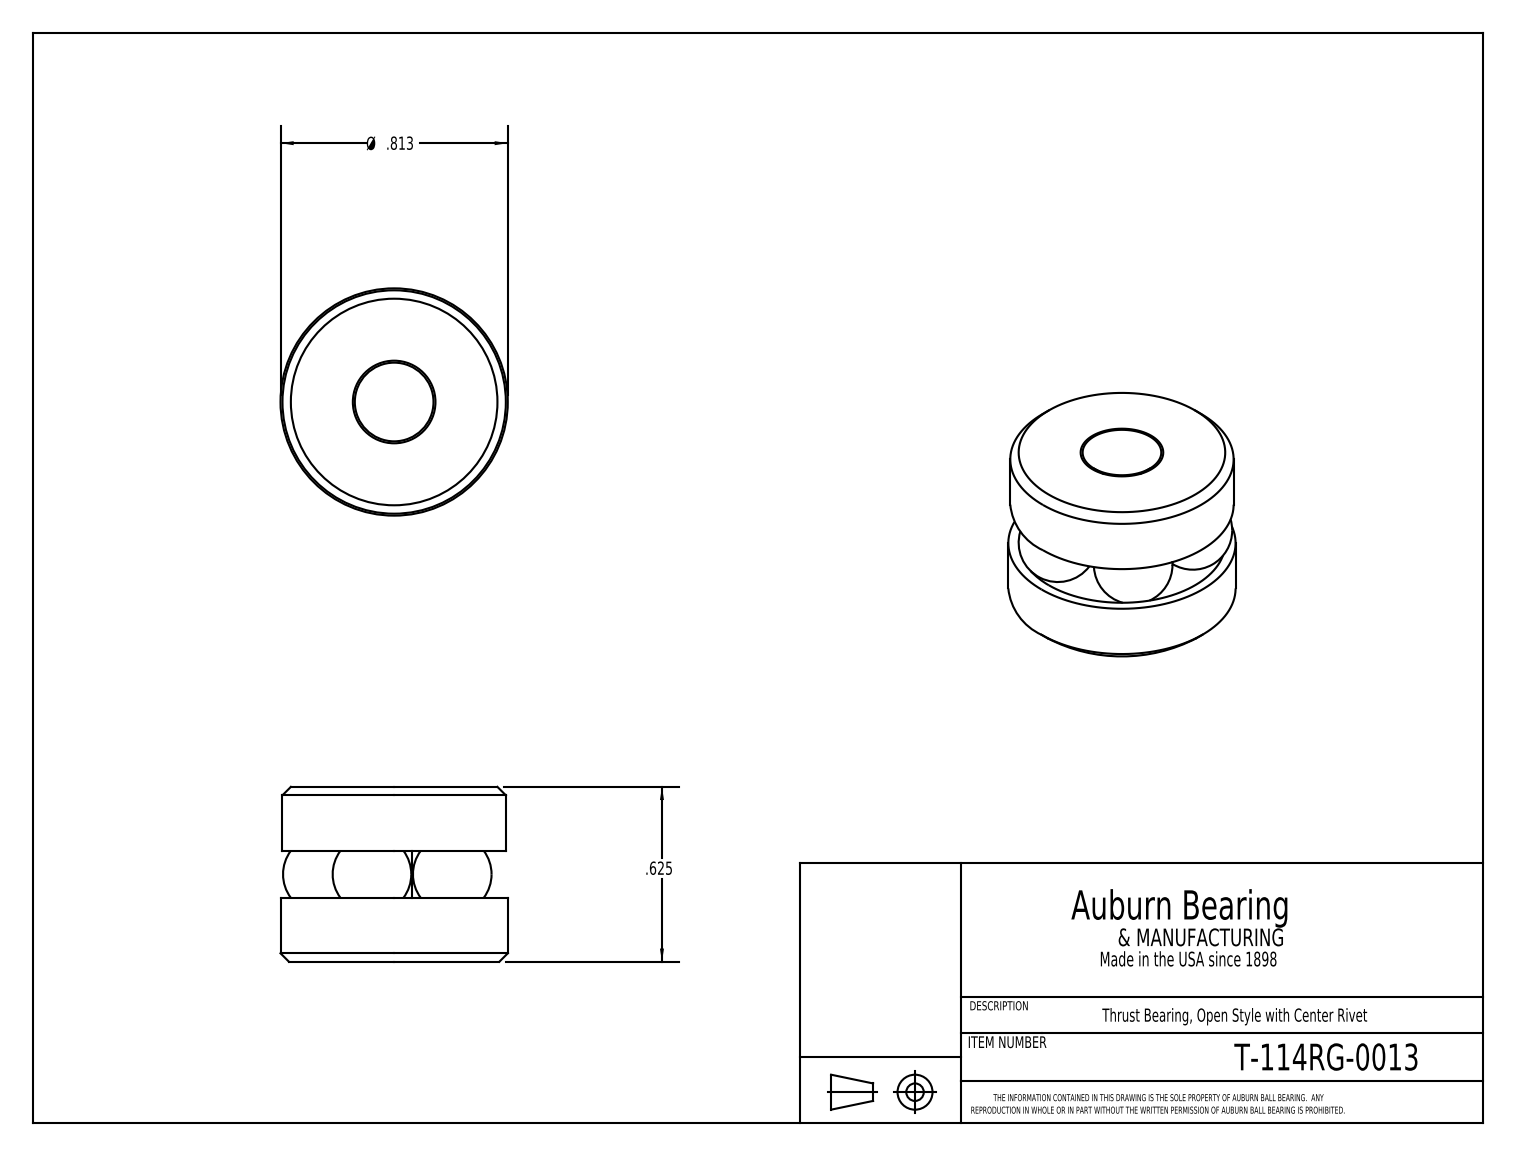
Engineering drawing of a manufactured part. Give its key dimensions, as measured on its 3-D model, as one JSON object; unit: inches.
{"part_name": "T-114RG_T-114RG-0013", "step_written_by": "SolidWorks 2016 (CONFIG_CONTROL_DESIGN)", "units": "inches", "bodies": {"solids": 8, "faces": 26, "planar": 8, "cylindrical": 5, "other": 13}, "overall_size": [0.813, 0.813, 0.625], "volume_in3": 0.261, "surface_area_in2": 5.02, "round_holes": [[0.135, 1]], "round_bosses_or_shafts": [[0.813, 1], [0.799, 1], [0.125, 1]], "face_to_face_distances": [0.625, 0.228, 0.397, 0.169]}
